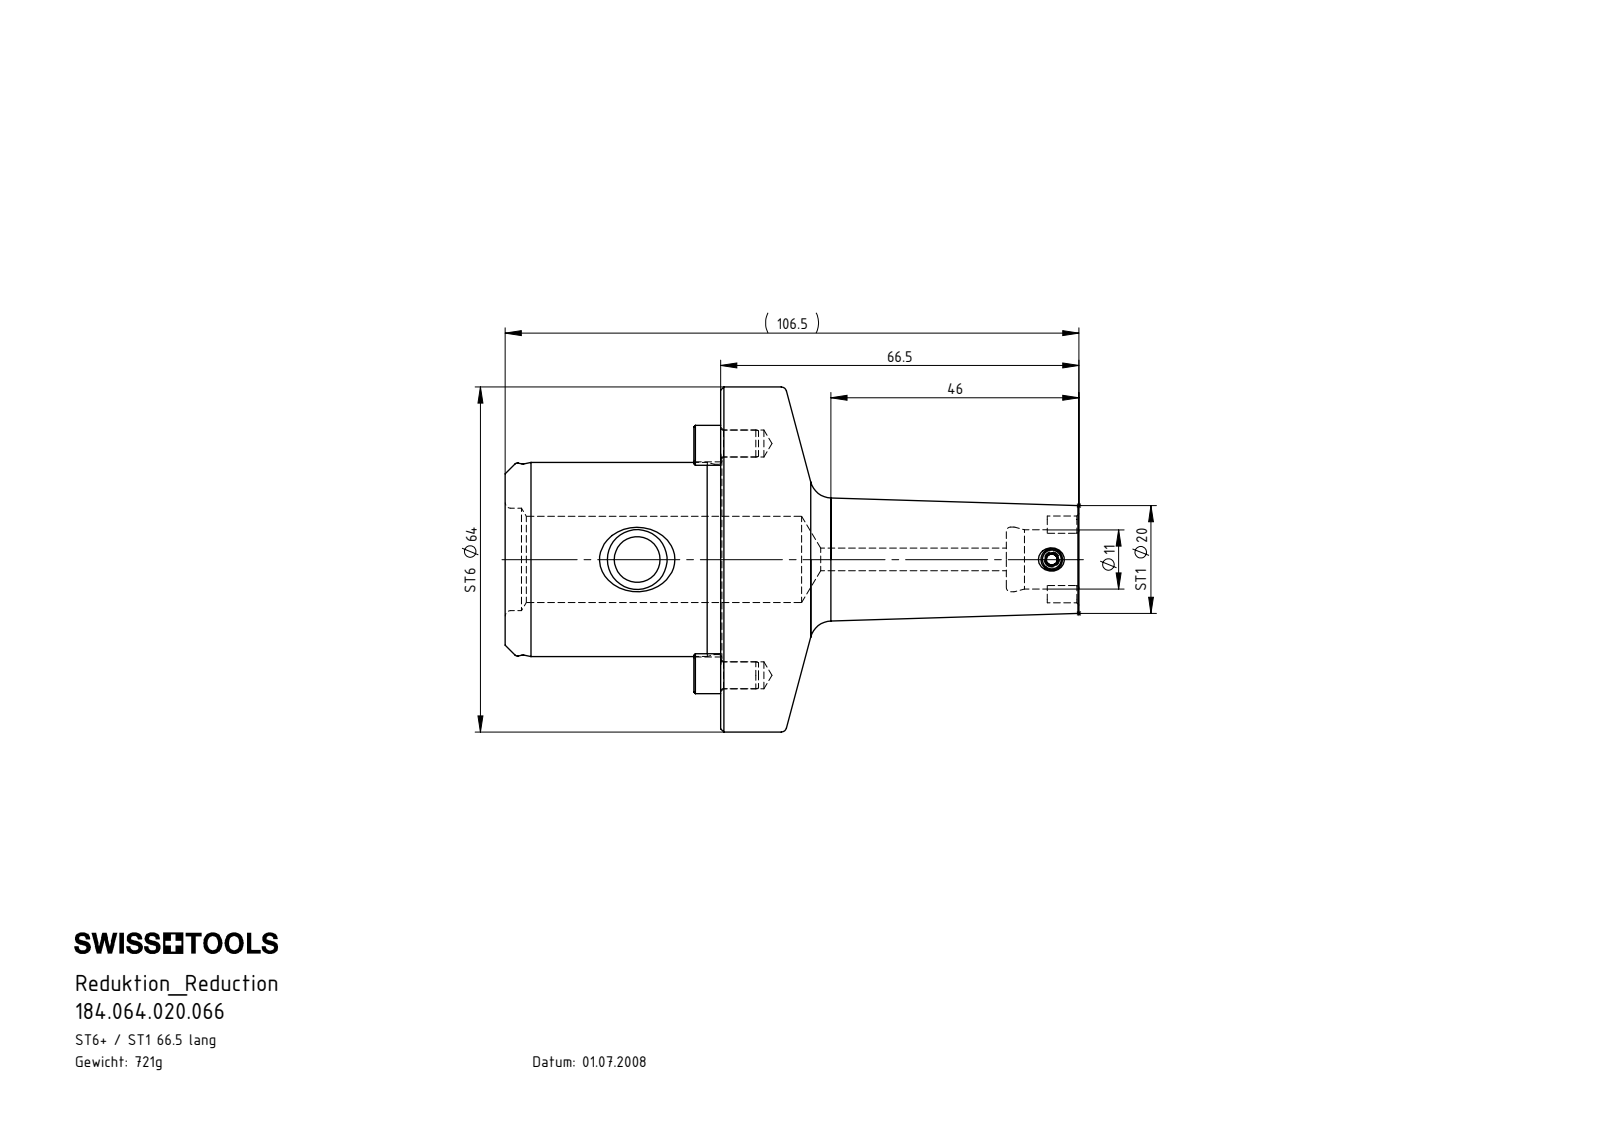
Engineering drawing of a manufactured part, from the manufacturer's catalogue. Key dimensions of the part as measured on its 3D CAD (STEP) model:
Part name (STEP PRODUCT): ST6-ER2.001.012_A; ST6-ST1.K01.066_A; ST1-ER1.001.005_A; ST6-ST1.K01.066
STEP written by: SolidWorks 2015 (CONFIG_CONTROL_DESIGN)
Units: millimetres
Bodies: 4 solids, 166 faces (26 planar, 47 cylindrical, 93 other)
Overall size (bounding box): 106.5 × 64 × 64
Volume: 91 885 mm³ · Surface area: 21 384 mm²
Round holes (diameter × count): ⌀5 ×2, ⌀3.5 ×1, ⌀4.2 ×1, ⌀8.5 ×1, ⌀11 ×1, ⌀12 ×1, ⌀16 ×1, ⌀19 ×1
Round bosses / shafts (diameter × count): ⌀64 ×1, ⌀36 ×1, ⌀35.8 ×1, ⌀35.3 ×1, ⌀4 ×1
Partial cylindrical surfaces — rounded edges, fillets, slot ends (radius × count): R0.5 ×4, R1.3 ×2, R5.47 ×2, R18.05 ×2
Main face-to-face distances: 40, 106.5, 66.5, 5, 35, 71.5, 93, 58, 53, 13.5
Hole centre spacings: 21.5, 43, 76.95
